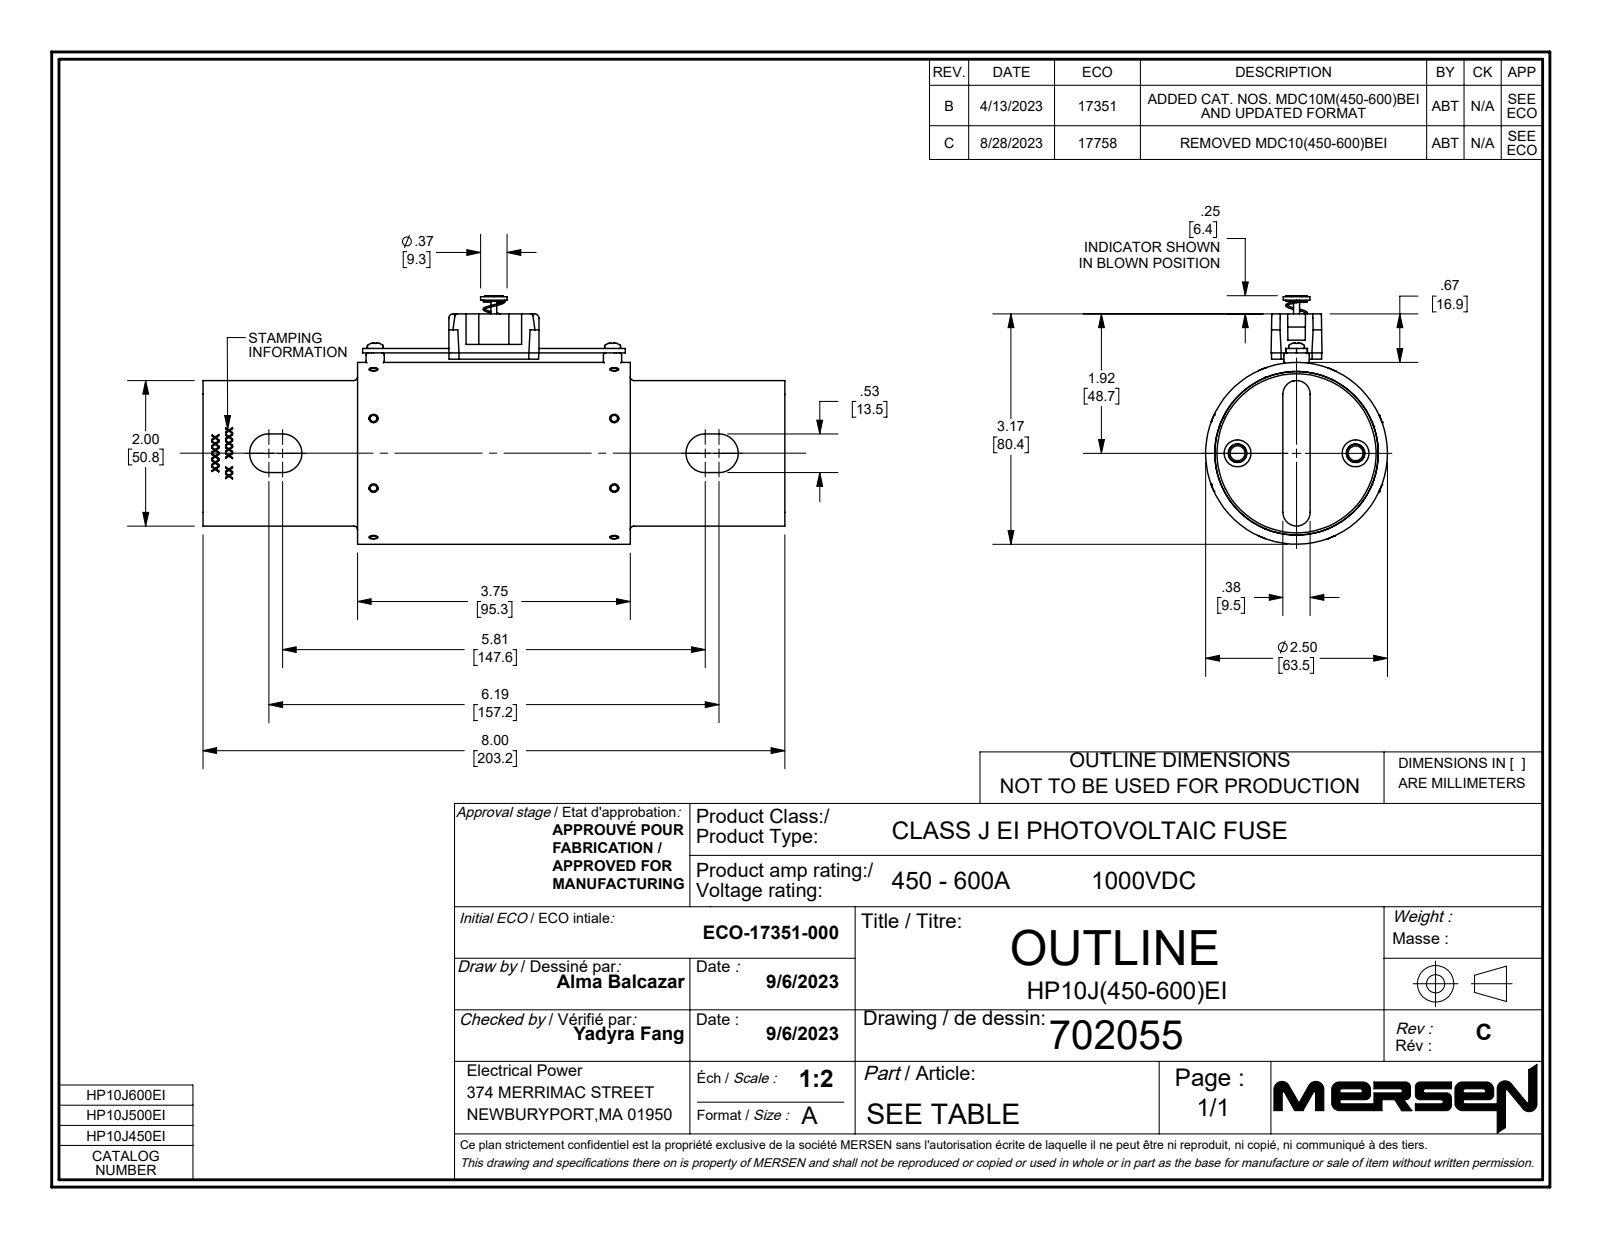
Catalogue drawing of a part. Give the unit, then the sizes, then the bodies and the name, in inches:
Units: inches
Overall size (bounding box): 8 × 3.416 × 2.5
Round holes (diameter × count): ⌀0.125 ×18, ⌀0.17 ×3, ⌀0.101 ×2, ⌀0.205 ×2, ⌀0.25 ×2, ⌀2.25 ×1
Round bosses / shafts (diameter × count): ⌀0.255 ×2, ⌀0.219 ×2, ⌀0.112 ×2, ⌀0.08 ×2, ⌀2.5 ×1, ⌀2.247 ×1, ⌀0.365 ×1, ⌀0.081 ×1
Partial cylindrical surfaces — rounded edges, fillets, slot ends (radius × count): R4 ×56, R0.03 ×20, R0.005 ×14, R0.02 ×10, R0.06 ×10, R0.05 ×6, R0.07 ×4, R0.15 ×4
Main face-to-face distances: 0.438, 3.312, 0.375, 3.75, 2.874, 0.25, 2.125, 2.563, 5.437, 5.875
Hole centre spacings: 3.31, 0.19, 0.812, 1.442, 1.632, 1.822, 0.38, 1.624
Volume: 10.08 in³ · Surface area: 121.4 in²
Bodies: 40 solids, 3004 faces (953 planar, 1206 cylindrical, 845 other)
Part name (STEP PRODUCT): 280253^340022; 702055; 23602_23602; 10310_10310 (+8 more)
STEP written by: SolidWorks 2021 (AUTOMOTIVE_DESIGN)
